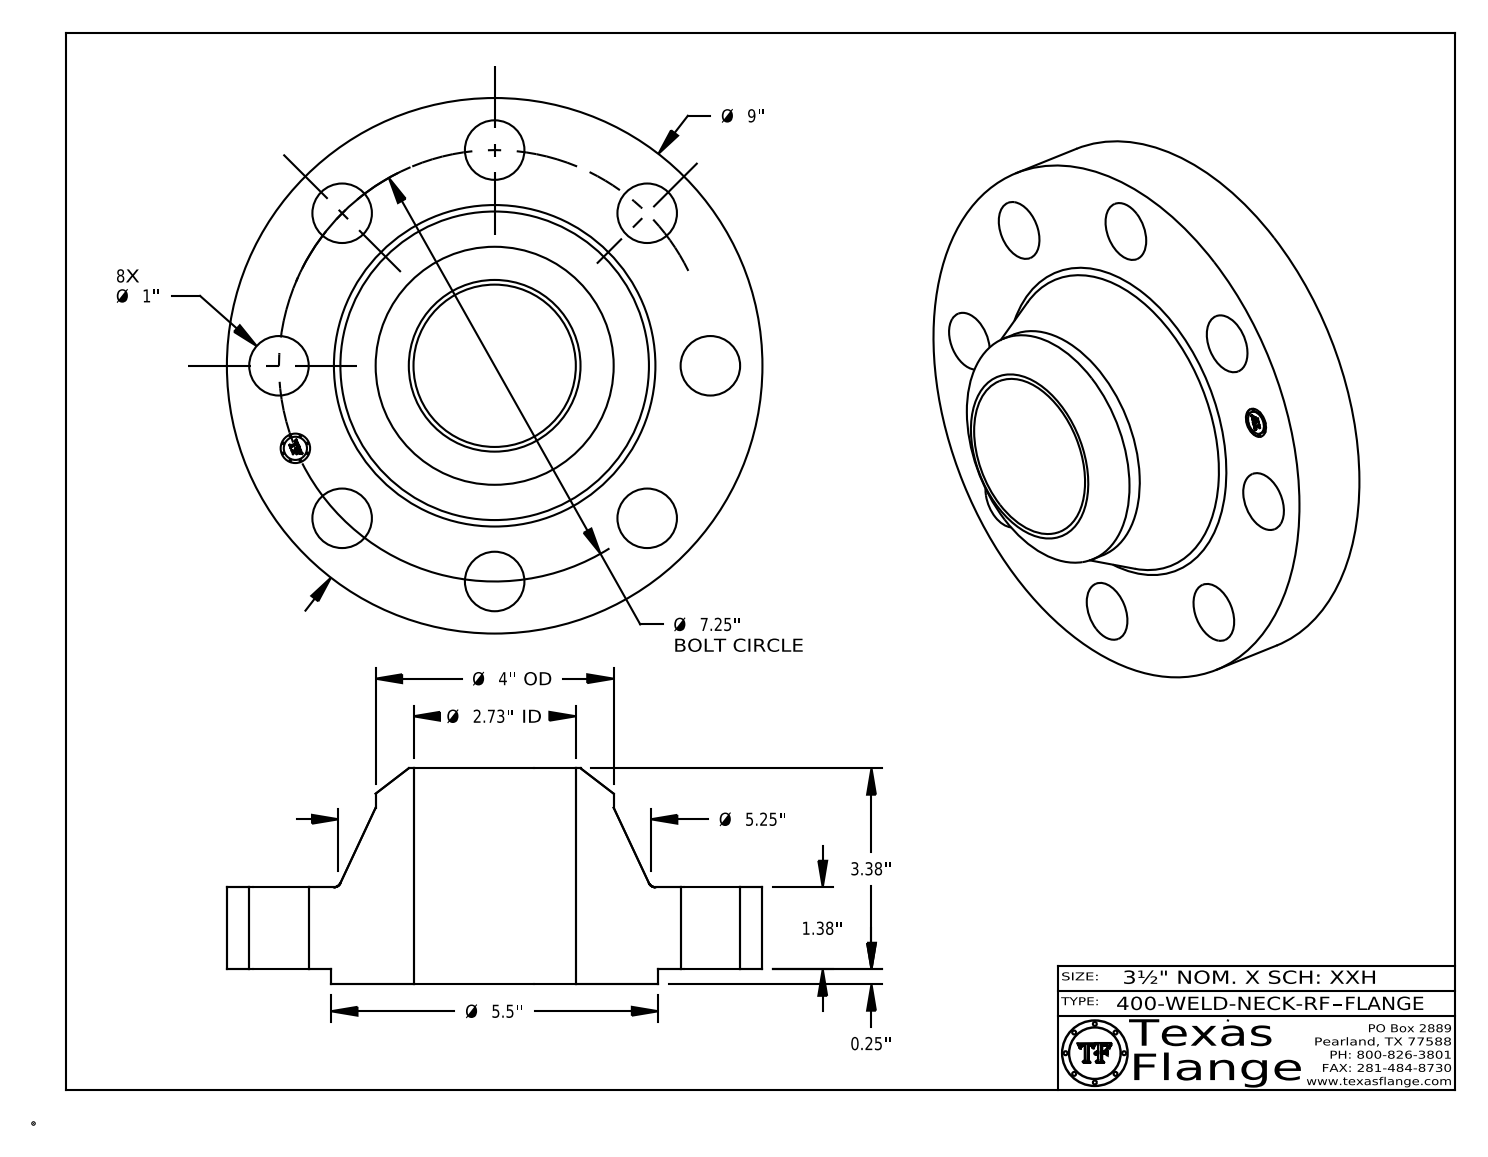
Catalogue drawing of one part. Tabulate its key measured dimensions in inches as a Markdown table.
| quantity | value |
| --- | --- |
| part name | 400-WELD-NECK-RF |
| STEP written by | CATIA V5 STEP AP214 (AUTOMOTIVE_DESIGN) |
| units | inches |
| bodies | 1 solid, 419 faces (369 planar, 44 cylindrical, 6 other) |
| overall size | 9 × 9 × 3.63 |
| volume | 93.43 in³ |
| surface area | 228.8 in² |
| round holes (diameter × count) | 1 × 8, 0.495 × 1, 2.728 × 1 |
| round bosses / shafts (diameter × count) | 0.03 × 8, 9 × 1, 5.5 × 1, 4 × 1, 0.39 × 1 |
| main face-to-face distances | 1.38, 0.25, 1.63, 3.63, 3.38, 2, 1.615, 1.365, 0.015, 2.015 |
| hole center spacings | 3.625, 2.774, 5.127, 6.698, 7.25, 1.415, 7.111, 4.028 |
